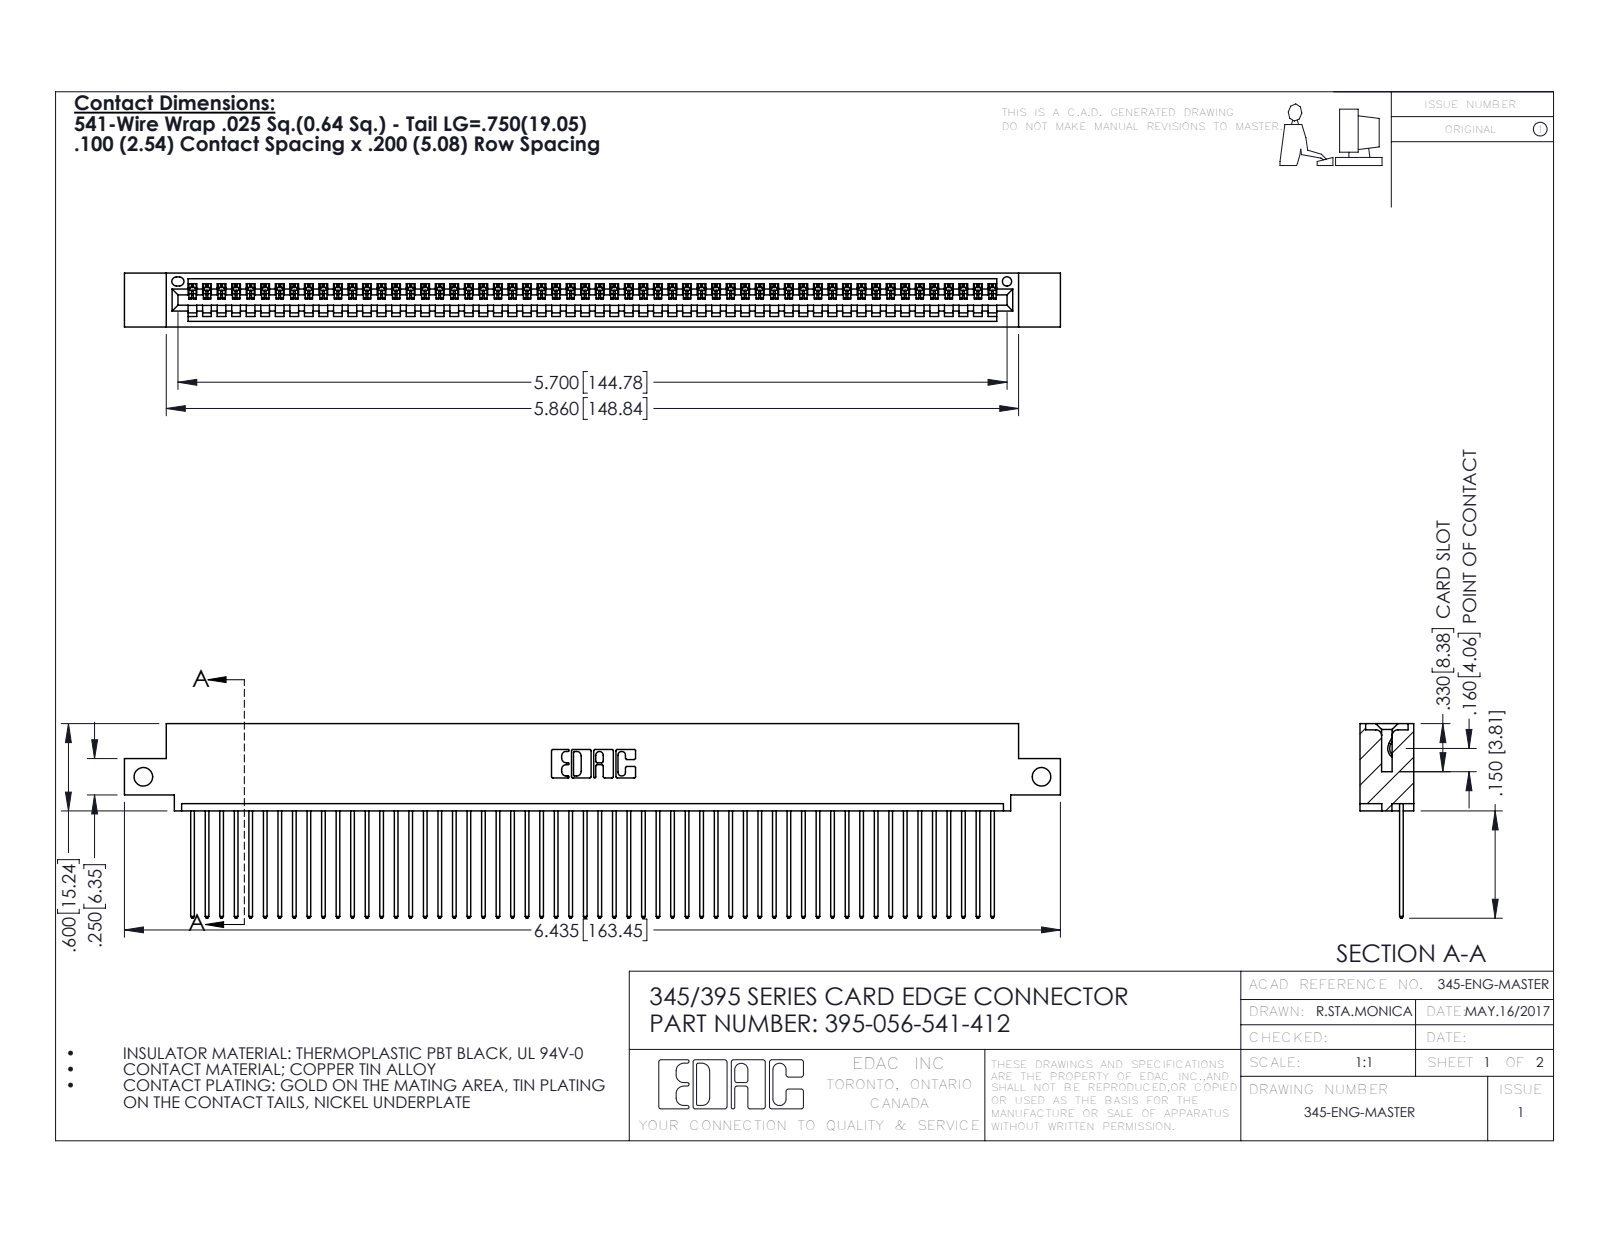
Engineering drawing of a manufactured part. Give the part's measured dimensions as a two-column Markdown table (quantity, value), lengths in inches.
| quantity | value |
| --- | --- |
| part name | 345-292-001_345-293-141; 395-056-541-412; 345 Part_0.110 Offset - Side Mount |
| STEP written by | SolidWorks 2016 (CONFIG_CONTROL_DESIGN) |
| units | inches |
| bodies | 57 solids, 3378 faces (2324 planar, 1054 cylindrical, 0 other) |
| overall size | 6.435 × 1.337 × 0.37 |
| volume | 0.956 in³ |
| surface area | 34.15 in² |
| round holes (diameter × count) | 0.128 × 2, 0.064 × 1 |
| partial cylindrical surfaces (radius × count) | 0.006 × 112, 0.01 × 112, 0.01 × 22, 0.007 × 6, 0.031 × 6, 0.026 × 3, 0.031 × 2, 0.04 × 2 |
| main face-to-face distances | 0.072, 0.298, 0.098, 0.272, 0.025, 0.37, 0.2, 0.225, 0.149, 0.072 |
| hole center spacings | 6.175 |
